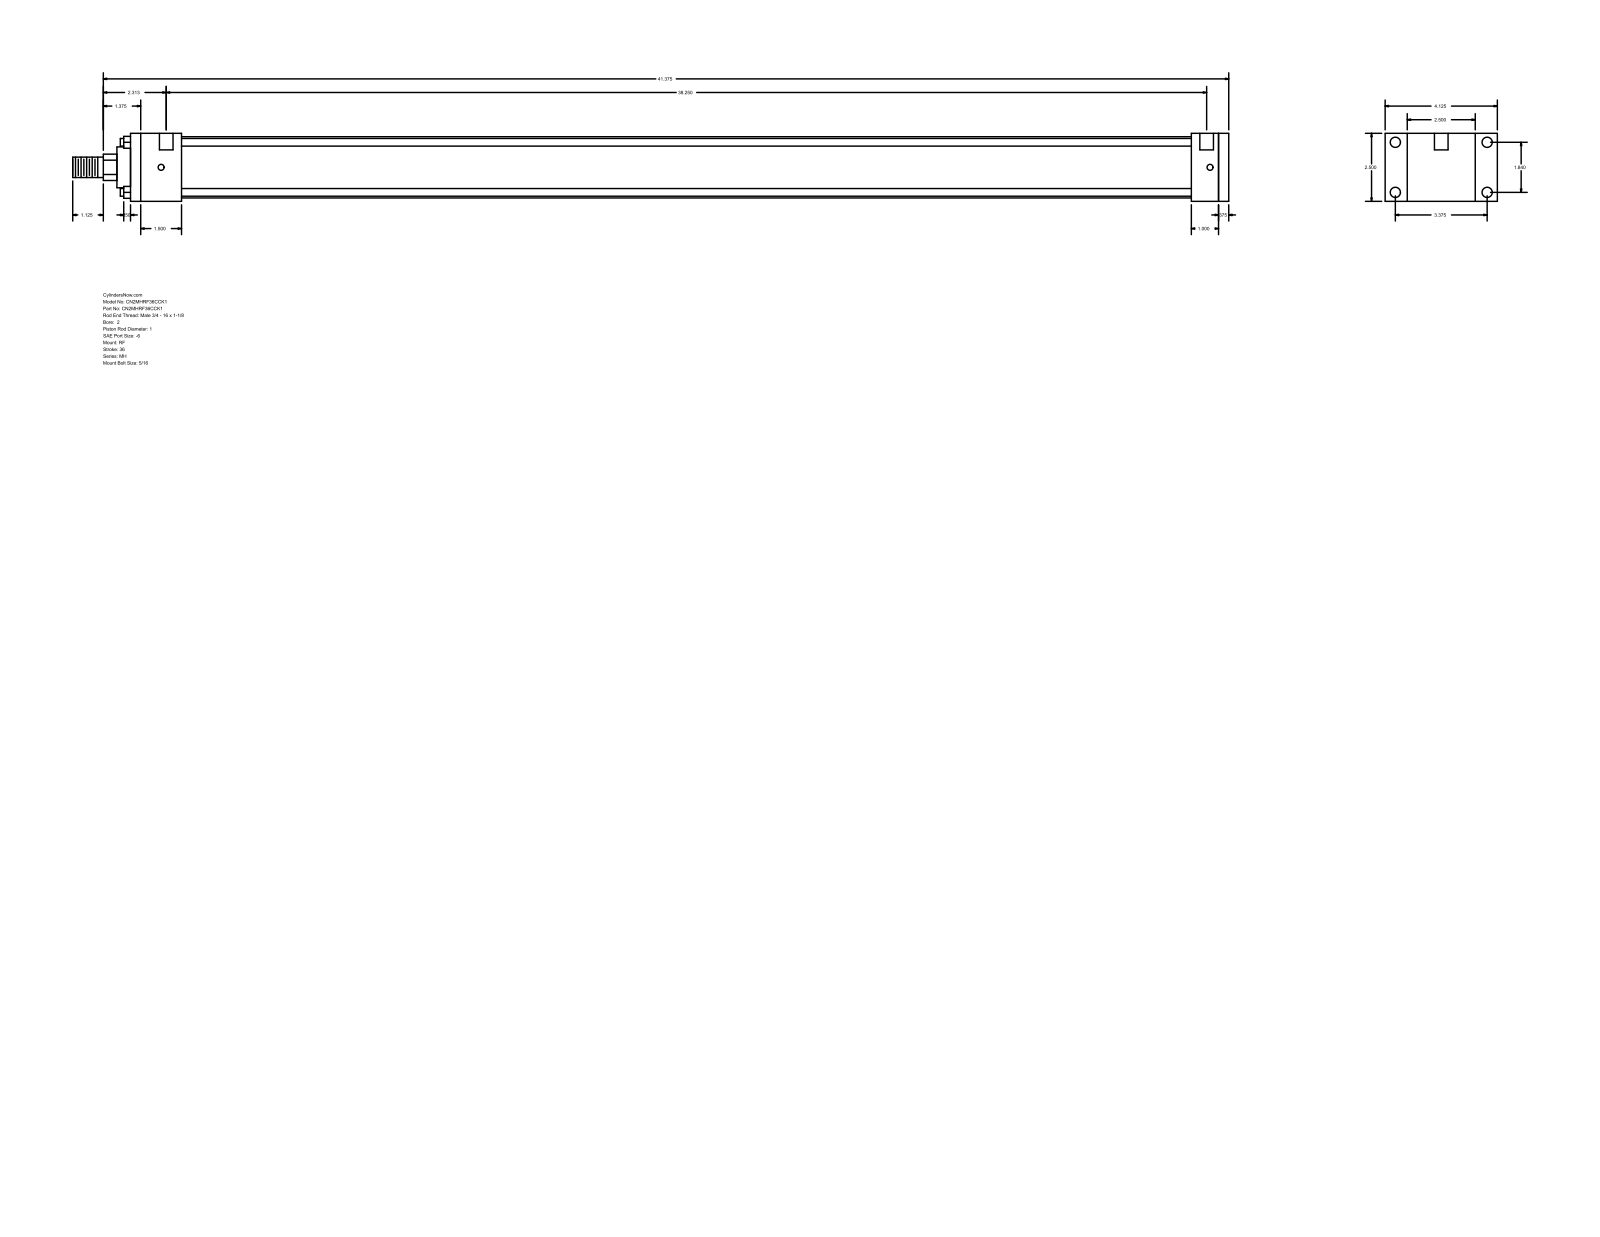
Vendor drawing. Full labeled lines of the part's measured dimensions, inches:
Part name (STEP PRODUCT): MH_RF__0200_1
STEP written by: GSSL Pune (CONFIG_CONTROL_DESIGN)
Units: inches
Bodies: 0 solids, 92 faces (64 planar, 28 cylindrical, 0 other)
Overall size (bounding box): 42.5 × 4.125 × 2.5
Round holes (diameter × count): ⌀0.219 ×4, ⌀0.375 ×4, ⌀0.5 ×2
Round bosses / shafts (diameter × count): ⌀0.281 ×4, ⌀2.25 ×1, ⌀1.5 ×1, ⌀1 ×1, ⌀0.75 ×1
Partial cylindrical surfaces — rounded edges, fillets, slot ends (radius × count): R0.484 ×1
Main face-to-face distances: 2.5, 40.375, 0.375, 40, 0.813, 1, 1.875, 39, 37.125, 38.125
Hole centre spacings: 1.84, 3.375, 3.844, 38.562, 0.125, 0.187, 38.25, 38.375
